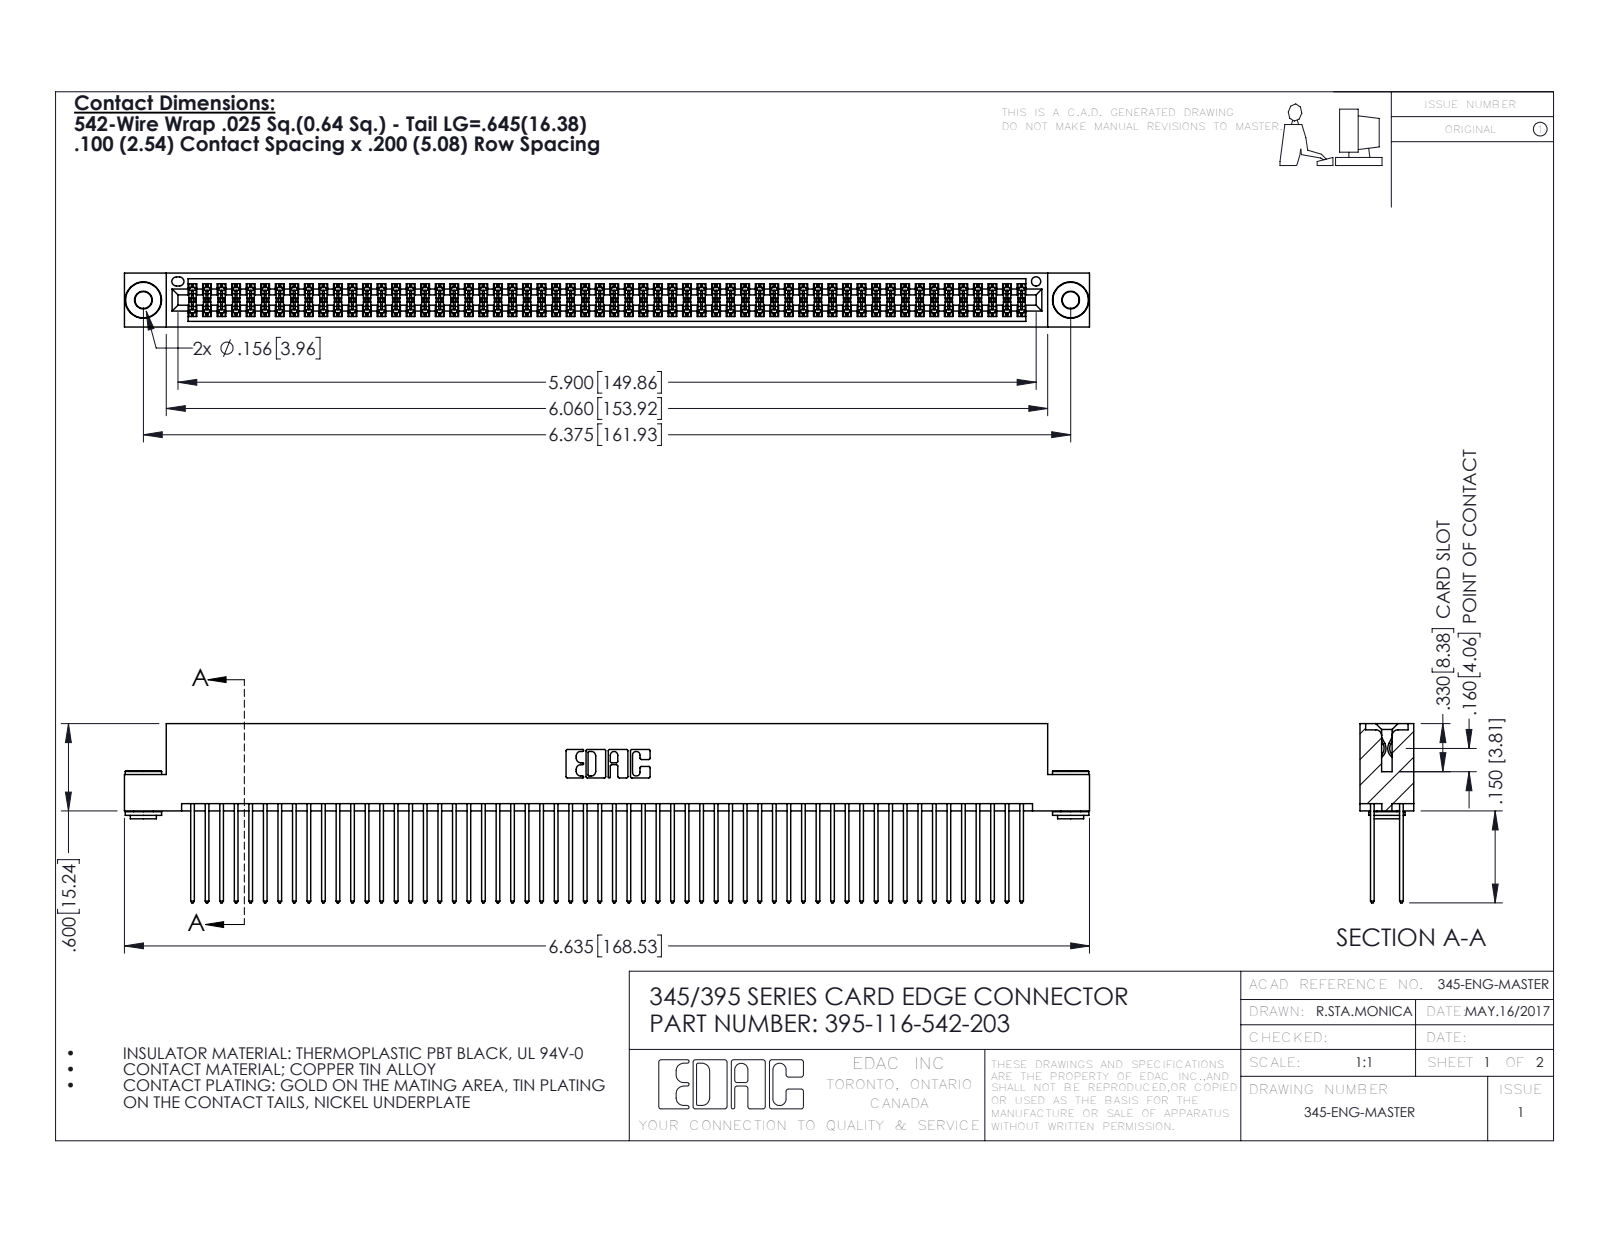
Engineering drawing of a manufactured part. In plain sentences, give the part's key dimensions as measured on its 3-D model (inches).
The part is named "395-116-542-203; 345 Part_Flush Mounting Lugs - 0.156 Dia-TH; 345-250-002_345-250-002-102; 345-292-001_345-293-142". Its 3-D file was written by "SolidWorks 2016 (CONFIG_CONTROL_DESIGN)". It is 119 solids with 5964 faces: 3918 planar, 2038 cylindrical and 8 other. Overall it measures 6.635 by 1.232 by 0.37 inches. Its volume is 1.042 cubic inches and its surface area 43.85 square inches. Round holes: 2 of diameter 0.116, 2 of diameter 0.156, 1 of diameter 0.064. Round bosses or shafts: 2 of diameter 0.25, 2 of diameter 0.18, 2 of diameter 0.136. Partial cylindrical surfaces (rounded edges, fillets, slot ends): 174 of radius 0.006, 116 of radius 0.01, 22 of radius 0.01, 6 of radius 0.007, 6 of radius 0.031, 3 of radius 0.026, 2 of radius 0.014, 2 of radius 0.019. The main face-to-face distances are 0.072, 0.298, 0.2, 0.025, 0.098, 0.272, 0.225, 0.37, 0.175, 0.149. The hole center spacings are 0.27, 6.139, 6.375.
